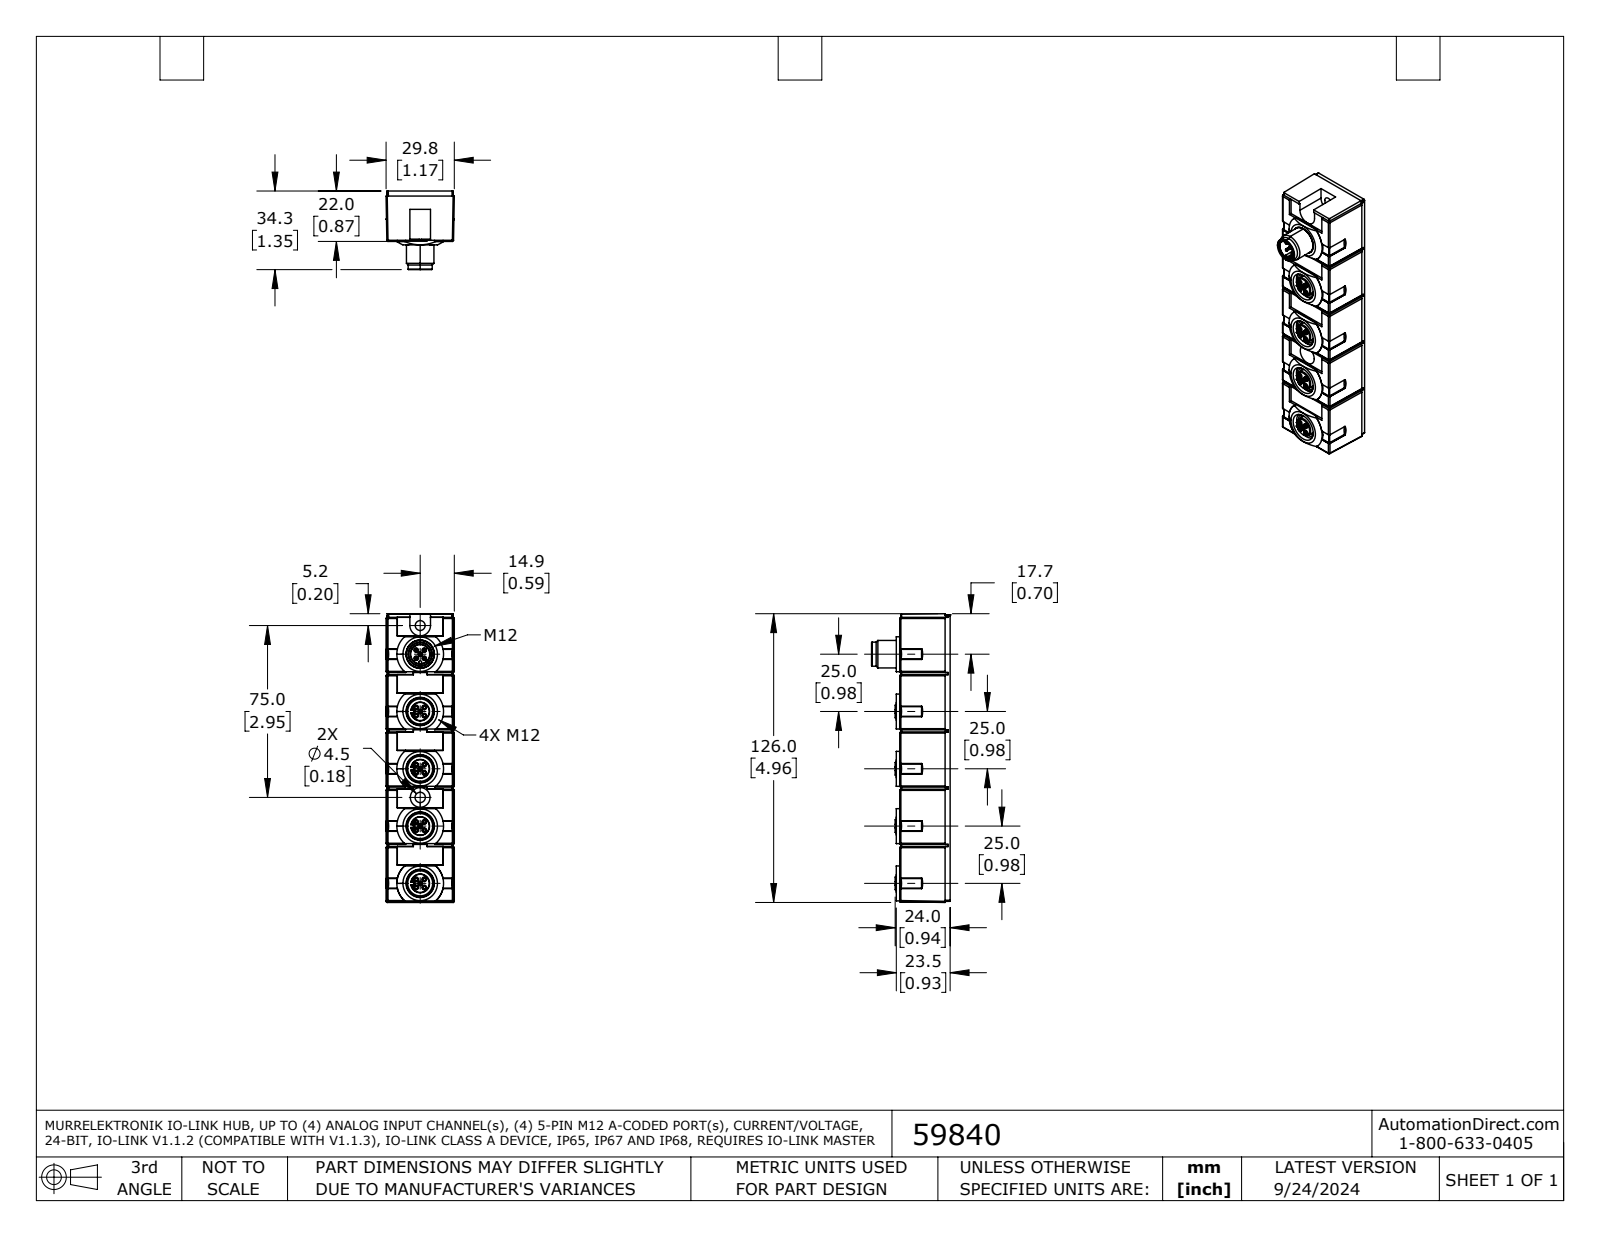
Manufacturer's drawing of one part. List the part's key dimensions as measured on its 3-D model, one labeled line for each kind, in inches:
Part name (STEP PRODUCT): 59840
STEP written by: SolidWorks 2021 (AUTOMOTIVE_DESIGN)
Units: inches
Bodies: 2 solids, 795 faces (264 planar, 345 cylindrical, 186 other)
Overall size (bounding box): 4.961 × 1.35 × 1.173
Volume: 4.865 in³ · Surface area: 27.56 in²
Round holes (diameter × count): ⌀0.047 ×20, ⌀0.049 ×5, ⌀0.075 ×5, ⌀0.486 ×5, ⌀0.43 ×3, ⌀0.169 ×1, ⌀0.177 ×1, ⌀0.327 ×1, ⌀0.339 ×1, ⌀0.43 ×1
Round bosses / shafts (diameter × count): ⌀0.079 ×20, ⌀0.039 ×5, ⌀0.323 ×4, ⌀0.484 ×1, ⌀0.472 ×1, ⌀0.413 ×1
Partial cylindrical surfaces — rounded edges, fillets, slot ends (radius × count): R0.02 ×36, R0.01 ×30, R0.394 ×20, R0.402 ×5, R0.024 ×4, R0.045 ×4, R0.012 ×2, R0.177 ×2
Main face-to-face distances: 0.866, 0.02, 0.039, 0.827, 0.098, 0.059, 0.079, 1.154, 0.925, 0.846
Hole centre spacings: 0.098, 0.139, 0.984, 0.917, 0.994, 1.056, 1.969, 1.9
